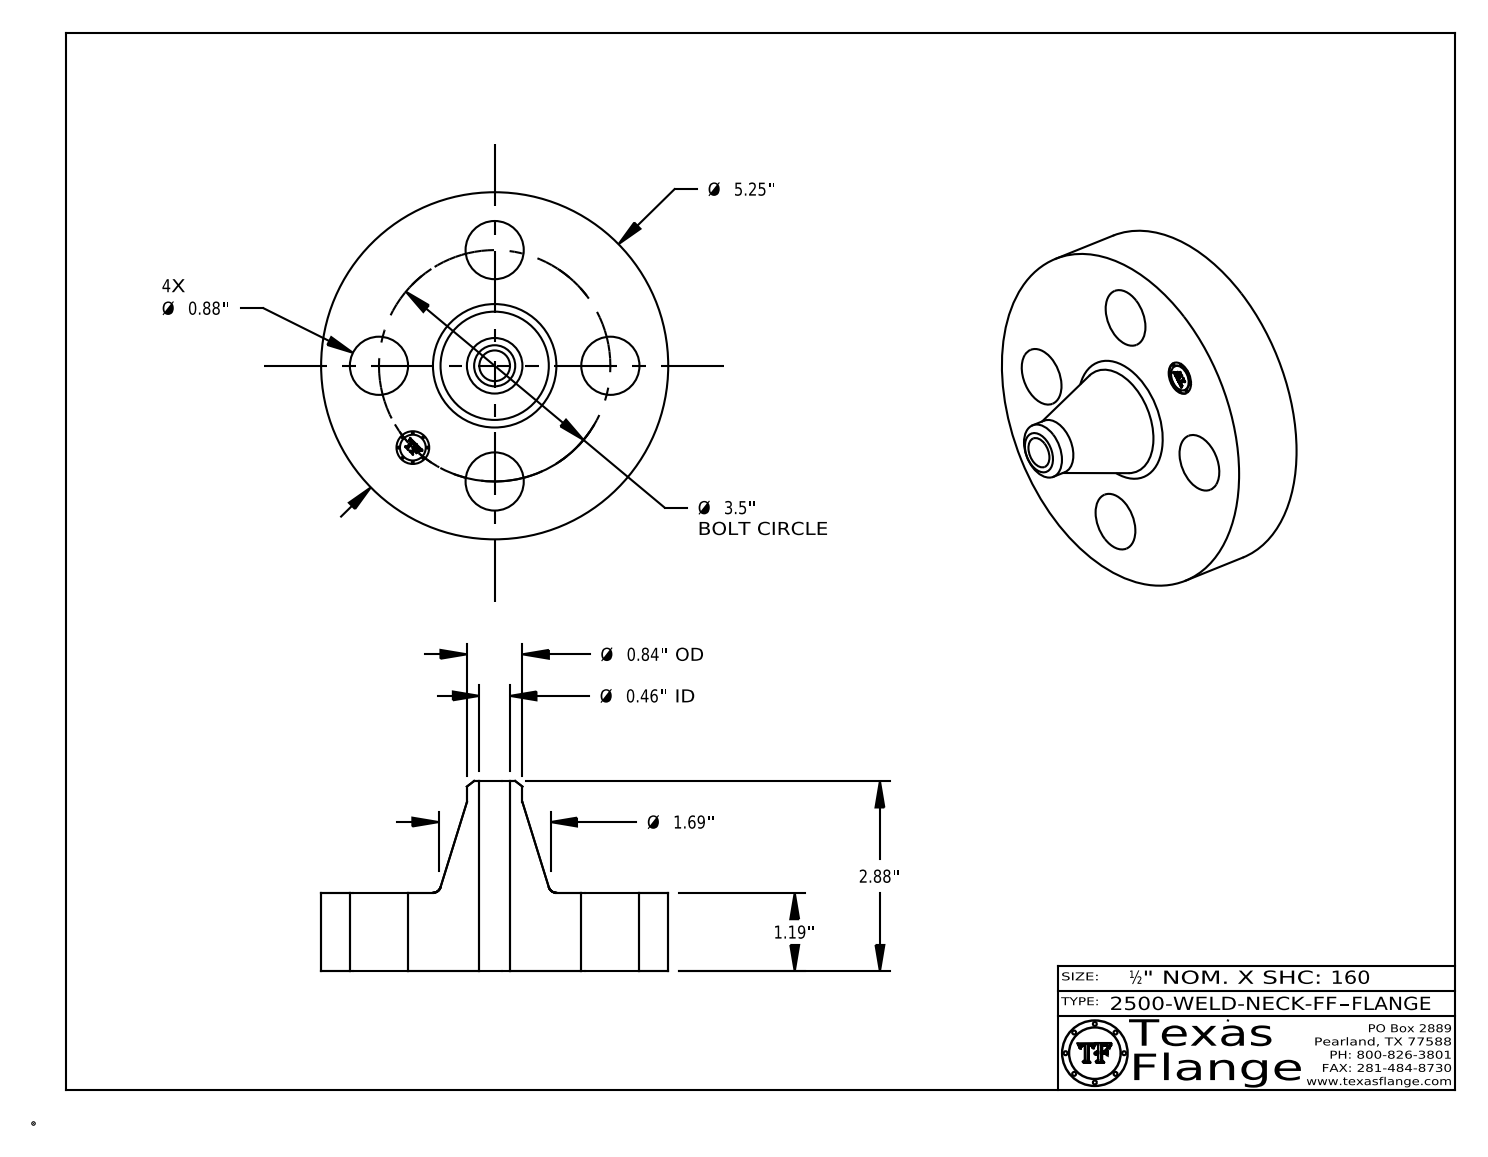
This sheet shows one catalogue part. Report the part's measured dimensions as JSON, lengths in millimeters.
{"part_name": "2500-WELD-NECK-FF", "step_written_by": "CATIA V5 STEP AP214 (AUTOMOTIVE_DESIGN)", "units": "millimeters", "bodies": {"solids": 1, "faces": 408, "planar": 368, "cylindrical": 34, "other": 6}, "overall_size": [133.4, 133.4, 73.2], "volume_mm3": 398900, "surface_area_mm2": 51450, "round_holes": [[22.4, 4], [11.8, 1], [12.6, 1]], "round_bosses_or_shafts": [[0.8, 8], [133.4, 1], [21.3, 1], [9.9, 1]], "face_to_face_distances": [30.2, 73.2, 42.9, 29.8, 0.4, 43.3, 3.8, 3.7, 0.7, 2.4], "hole_center_spacings": [44.5, 62.9, 34, 82.1, 88.9]}
